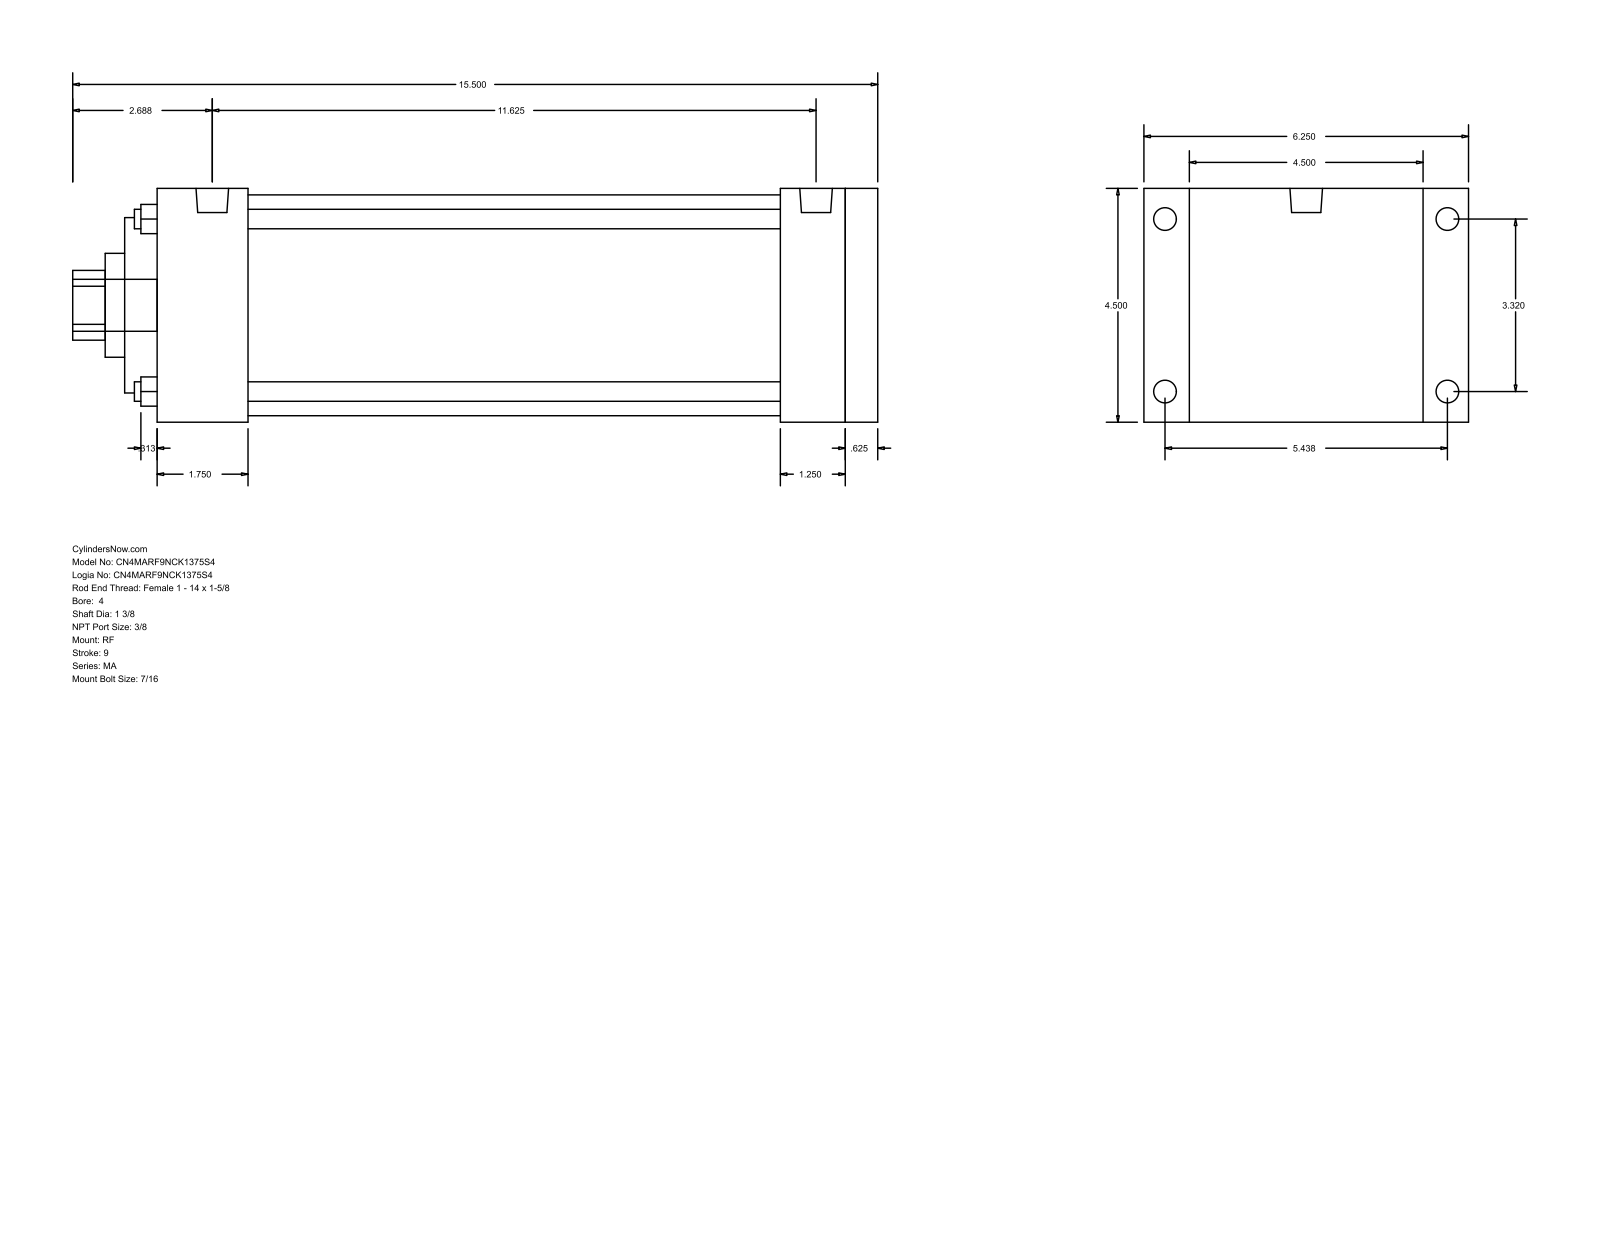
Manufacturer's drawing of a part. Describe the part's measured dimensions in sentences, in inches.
The part is named "MA_RF__0400_1.375". Its 3-D file was written by "GSSL Pune (CONFIG_CONTROL_DESIGN)". It is 0 solids with 94 faces: 65 planar, 29 cylindrical and 0 other. Overall it measures 15.5 by 6.25 by 4.5 inches. Round holes: 4 of diameter 0.375, 1 of diameter 1.375, 1 of diameter 2, 1 of diameter 3.375, 1 of diameter 4.25. Round bosses or shafts: 8 of diameter 0.437, 2 of diameter 0.627, 1 of diameter 1. Partial cylindrical surfaces (rounded edges, fillets, slot ends): 1 of radius 0.672. The main face-to-face distances are 4.5, 13.875, 0.625, 13.25, 0.625, 13.875, 14.5, 0.875, 5.375, 12.625. The hole center spacings are 2.347, 3.32, 4.695.
